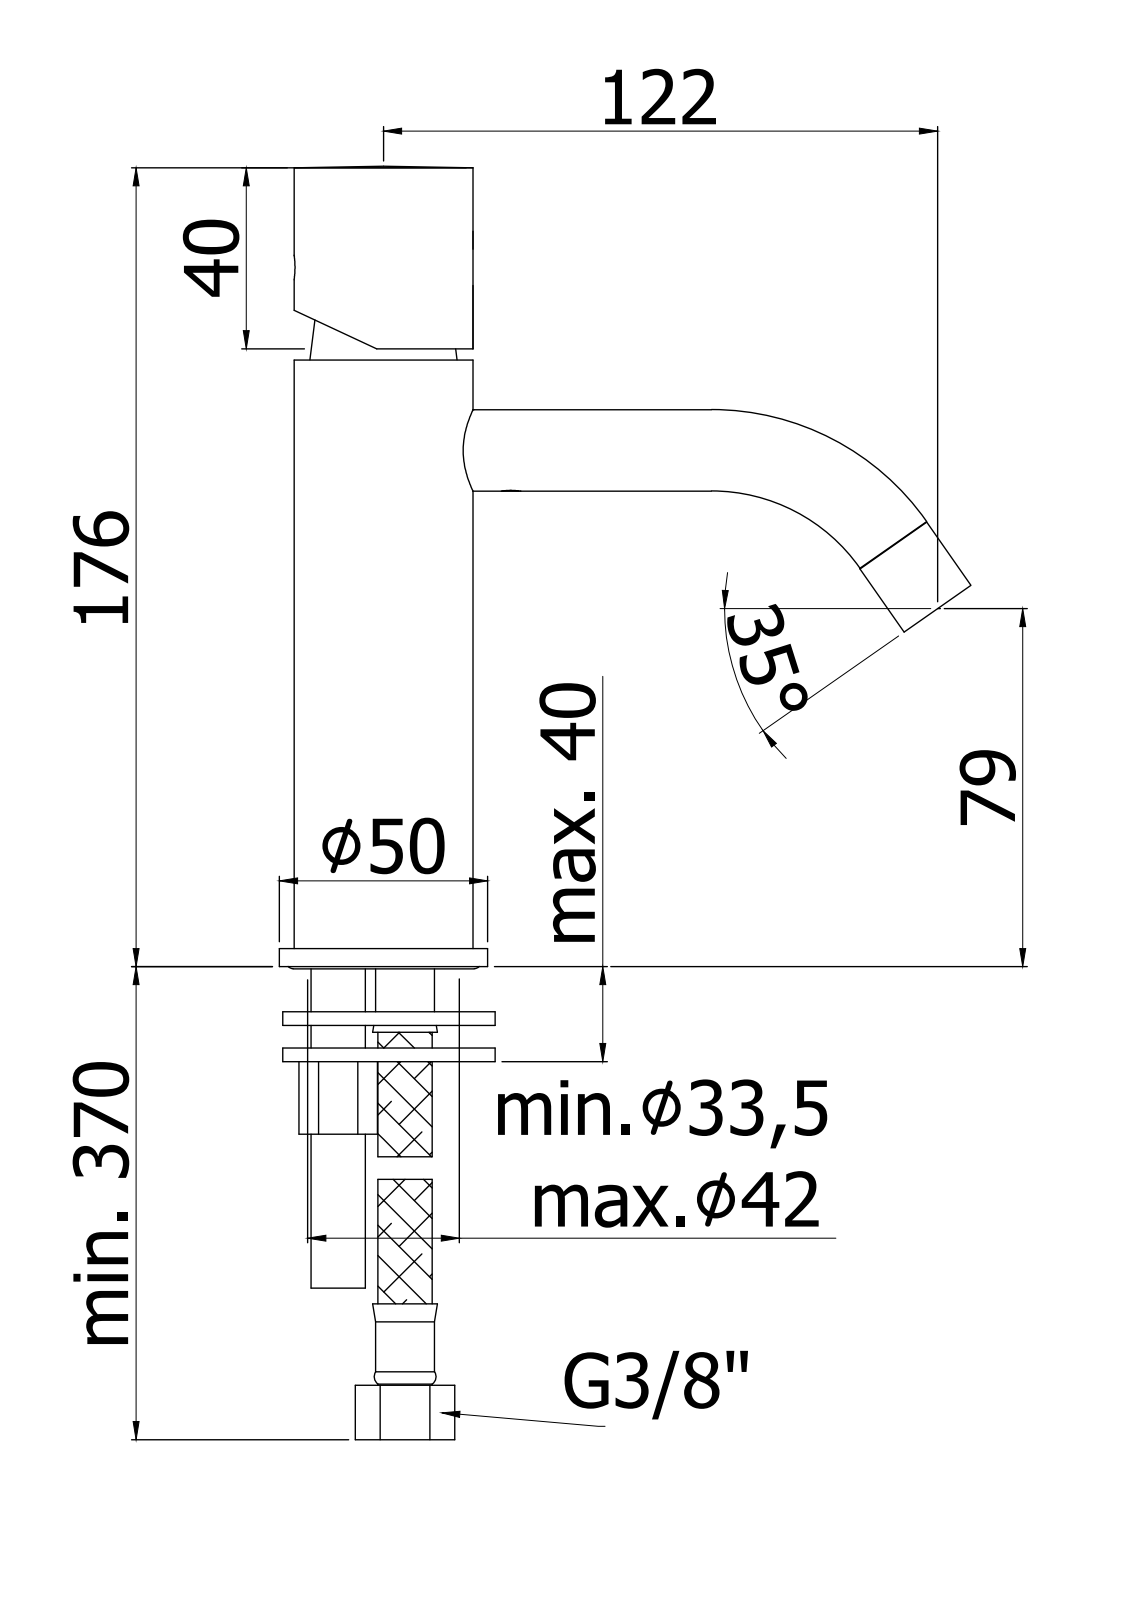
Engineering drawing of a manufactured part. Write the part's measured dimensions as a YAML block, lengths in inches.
part_name: "LIGX071CR"
step_written_by: "CREO PARAMETRIC BY PTC INC, 2020044 (CONFIG_CONTROL_DESIGN)"
units: inches
bodies: {solids: 2, faces: 213, planar: 57, cylindrical: 82, other: 74}
overall_size: [6.905, 6.12, 1.969]
volume: 9.114
surface_area: 97.48
round_holes:
  - {diameter: 0.433, count: 4}
  - {diameter: 0.394, count: 3}
  - {diameter: 0.126, count: 2}
  - {diameter: 0.197, count: 2}
  - {diameter: 0.354, count: 2}
  - {diameter: 0.118, count: 1}
  - {diameter: 0.165, count: 1}
  - {diameter: 0.217, count: 1}
  - {diameter: 0.268, count: 1}
  - {diameter: 0.492, count: 1}
  - {diameter: 0.551, count: 1}
  - {diameter: 1.008, count: 1}
round_bosses_or_shafts:
  - {diameter: 0.709, count: 2}
  - {diameter: 1.969, count: 1}
  - {diameter: 1.555, count: 1}
  - {diameter: 0.299, count: 1}
partial_cylinders:
  - {radius: 0.453, count: 1}
  - {radius: 0.776, count: 1}
face_to_face_distances: [0.157, 0.157, 6.773, 6.772, 6.616, 0.394, 0.551, 5.118, 0.55, 6.222]
hole_center_spacings: [0.394, 0.108, 0.169, 0.265, 0.345, 0.35, 0.352, 0.367]
